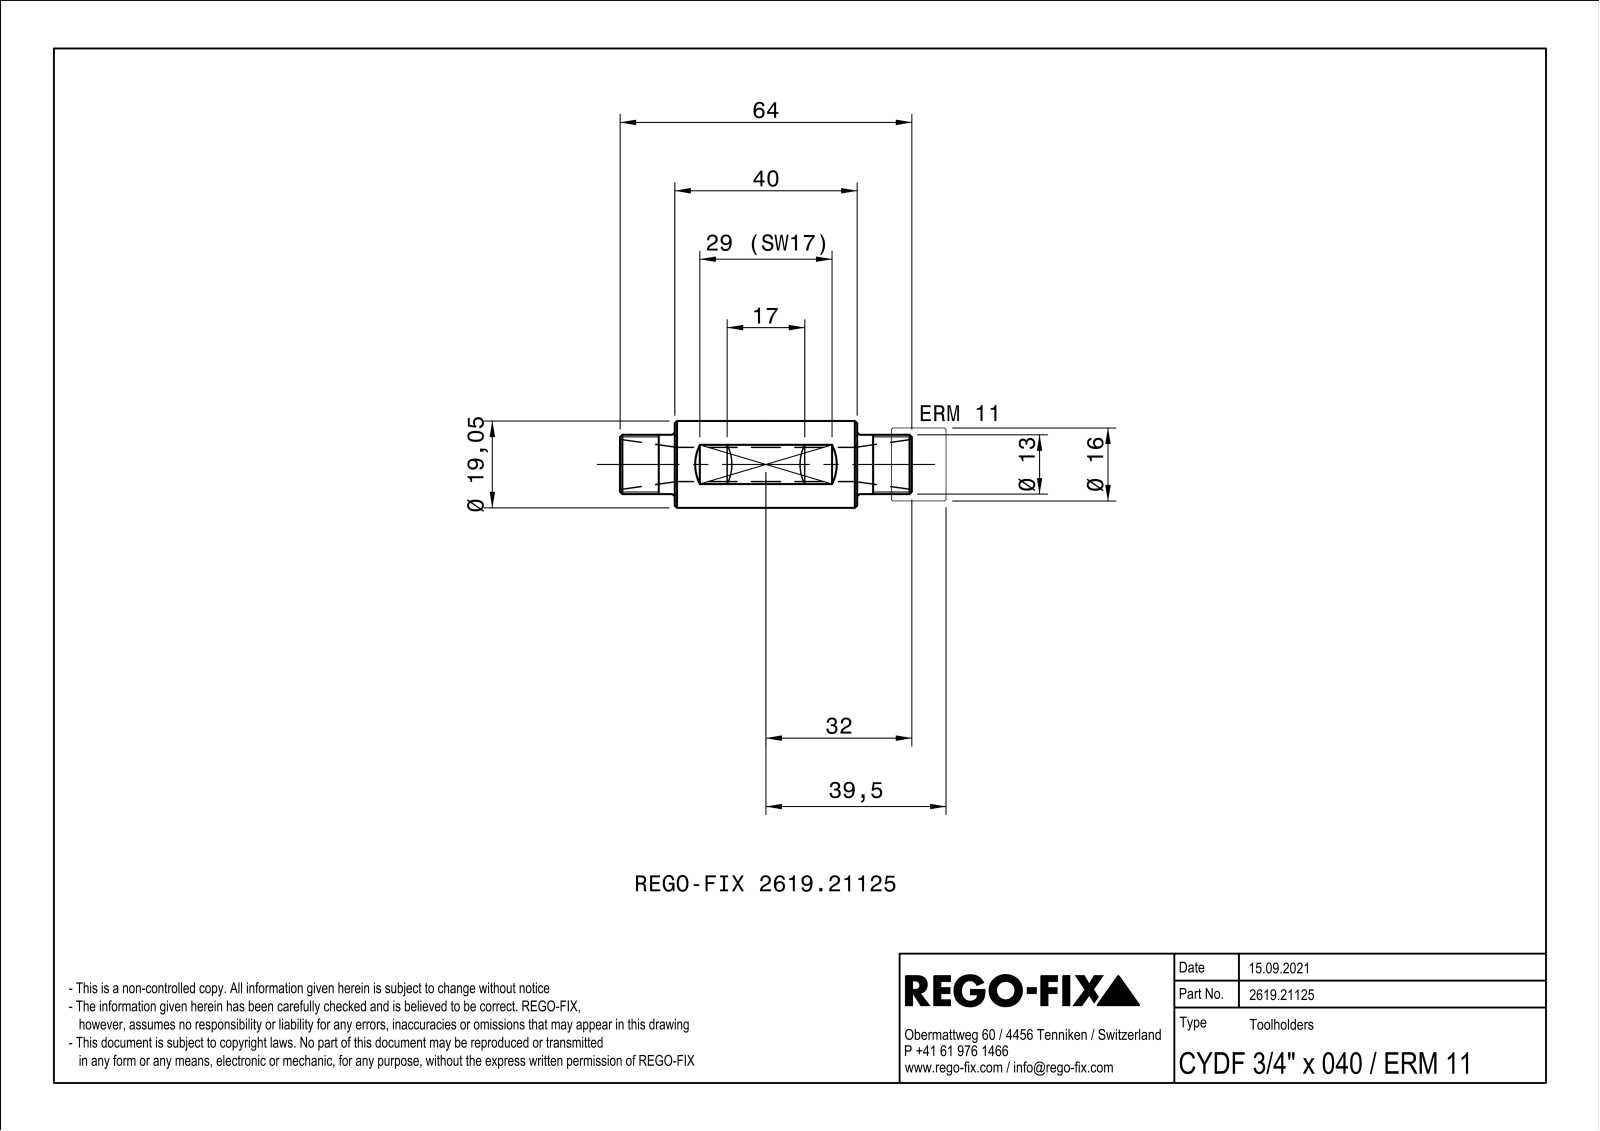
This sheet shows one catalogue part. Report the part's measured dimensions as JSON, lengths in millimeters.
{"part_name": "NOCUT", "step_written_by": "SIEMENS PLM Software Solid Edge ST10 (AUTOMOTIVE_DESIGN)", "units": "millimeters", "bodies": {"solids": 1, "faces": 29, "planar": 13, "cylindrical": 6, "other": 10}, "overall_size": [64, 19.05, 19.05], "volume_mm3": 10893, "surface_area_mm2": 5313, "round_holes": [[7.5, 1]], "round_bosses_or_shafts": [[19.05, 1], [13, 1]], "face_to_face_distances": [17, 40, 12, 52, 8.48, 7.78, 16.26, 64]}
